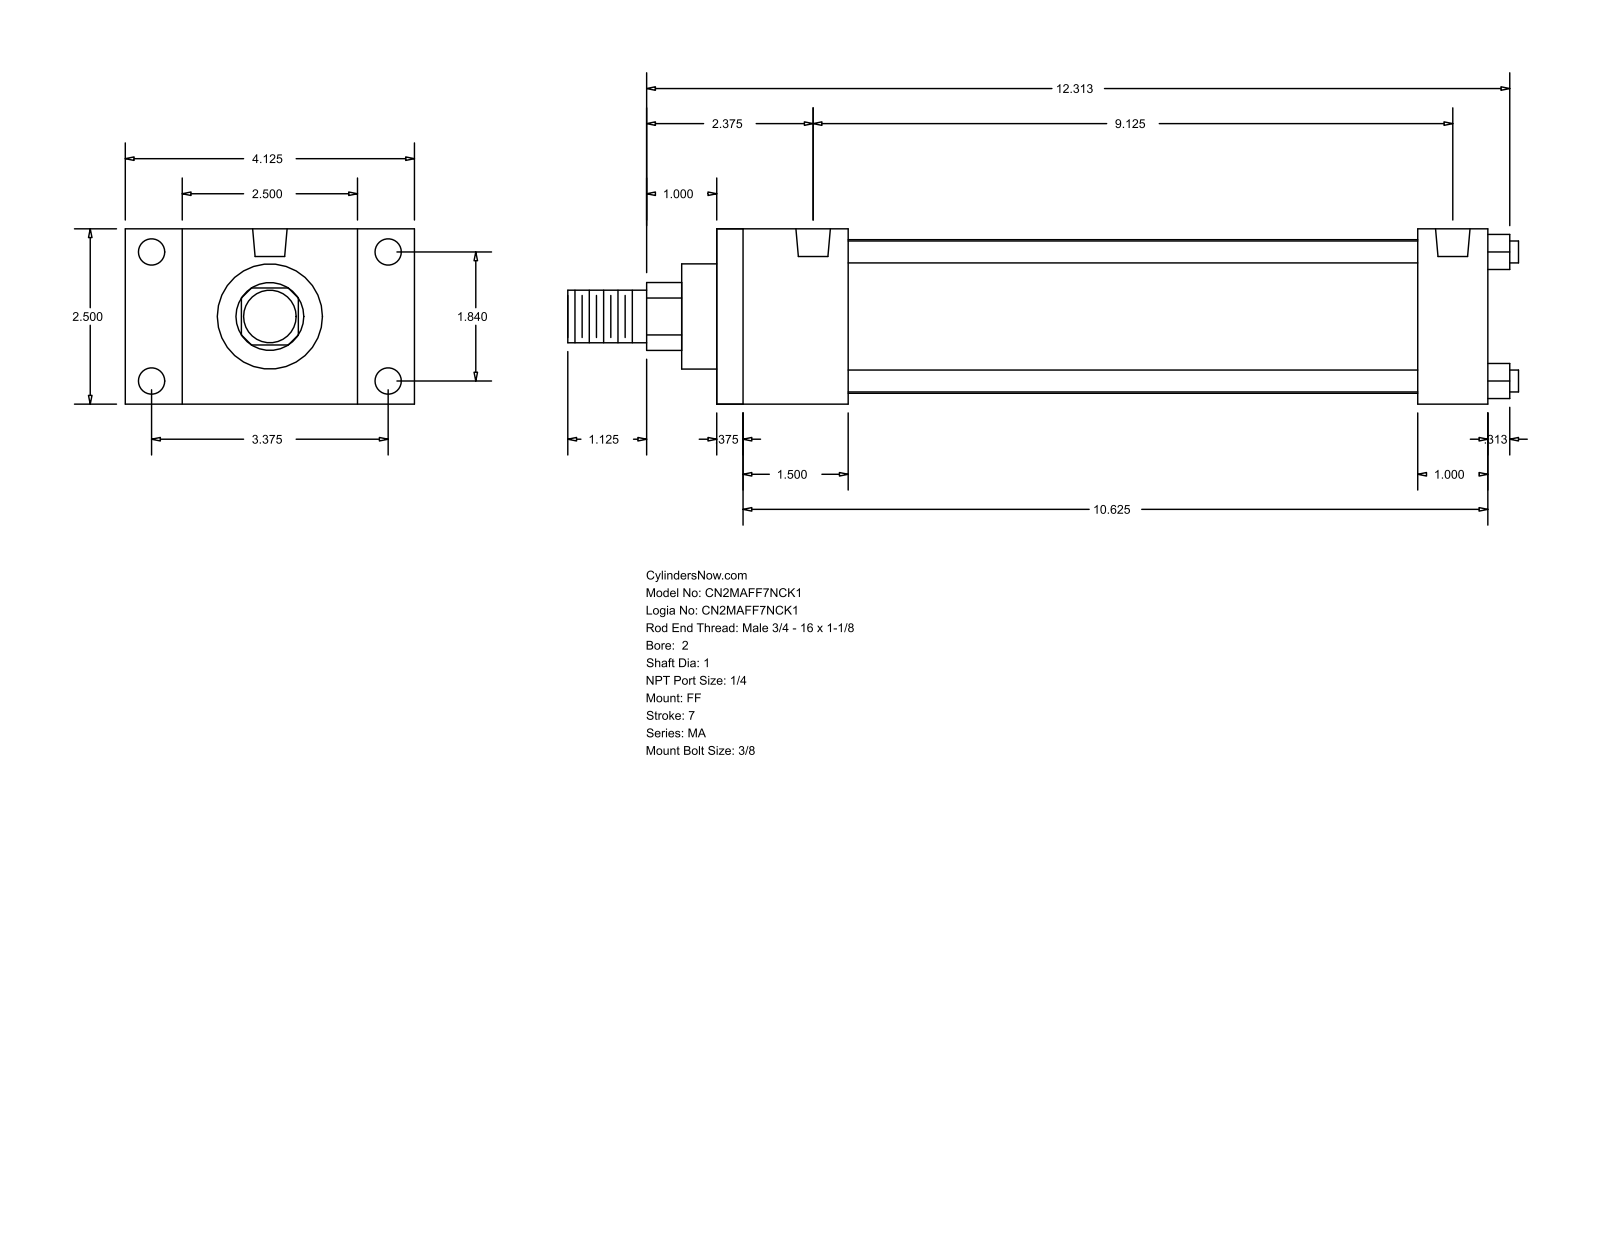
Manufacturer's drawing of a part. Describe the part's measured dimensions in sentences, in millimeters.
The part is named "MA_FF__0200_1". Its 3-D file was written by "GSSL Pune (CONFIG_CONTROL_DESIGN)". It is 0 solids with 92 faces: 64 planar, 28 cylindrical and 0 other. Overall it measures 344.49 by 104.78 by 63.5 millimeters. Round holes: 4 of diameter 7.94, 4 of diameter 9.53, 2 of diameter 12.49. Round bosses or shafts: 4 of diameter 7.94, 1 of diameter 55.63, 1 of diameter 38.1, 1 of diameter 25.4, 1 of diameter 19.05. Partial cylindrical surfaces (rounded edges, fillets, slot ends): 1 of radius 12.29. The main face-to-face distances are 63.5, 279.4, 9.52, 269.88, 25.4, 20.64, 12.7, 47.63, 254, 38.11. The hole center spacings are 46.74, 85.72, 97.63, 231.77.
